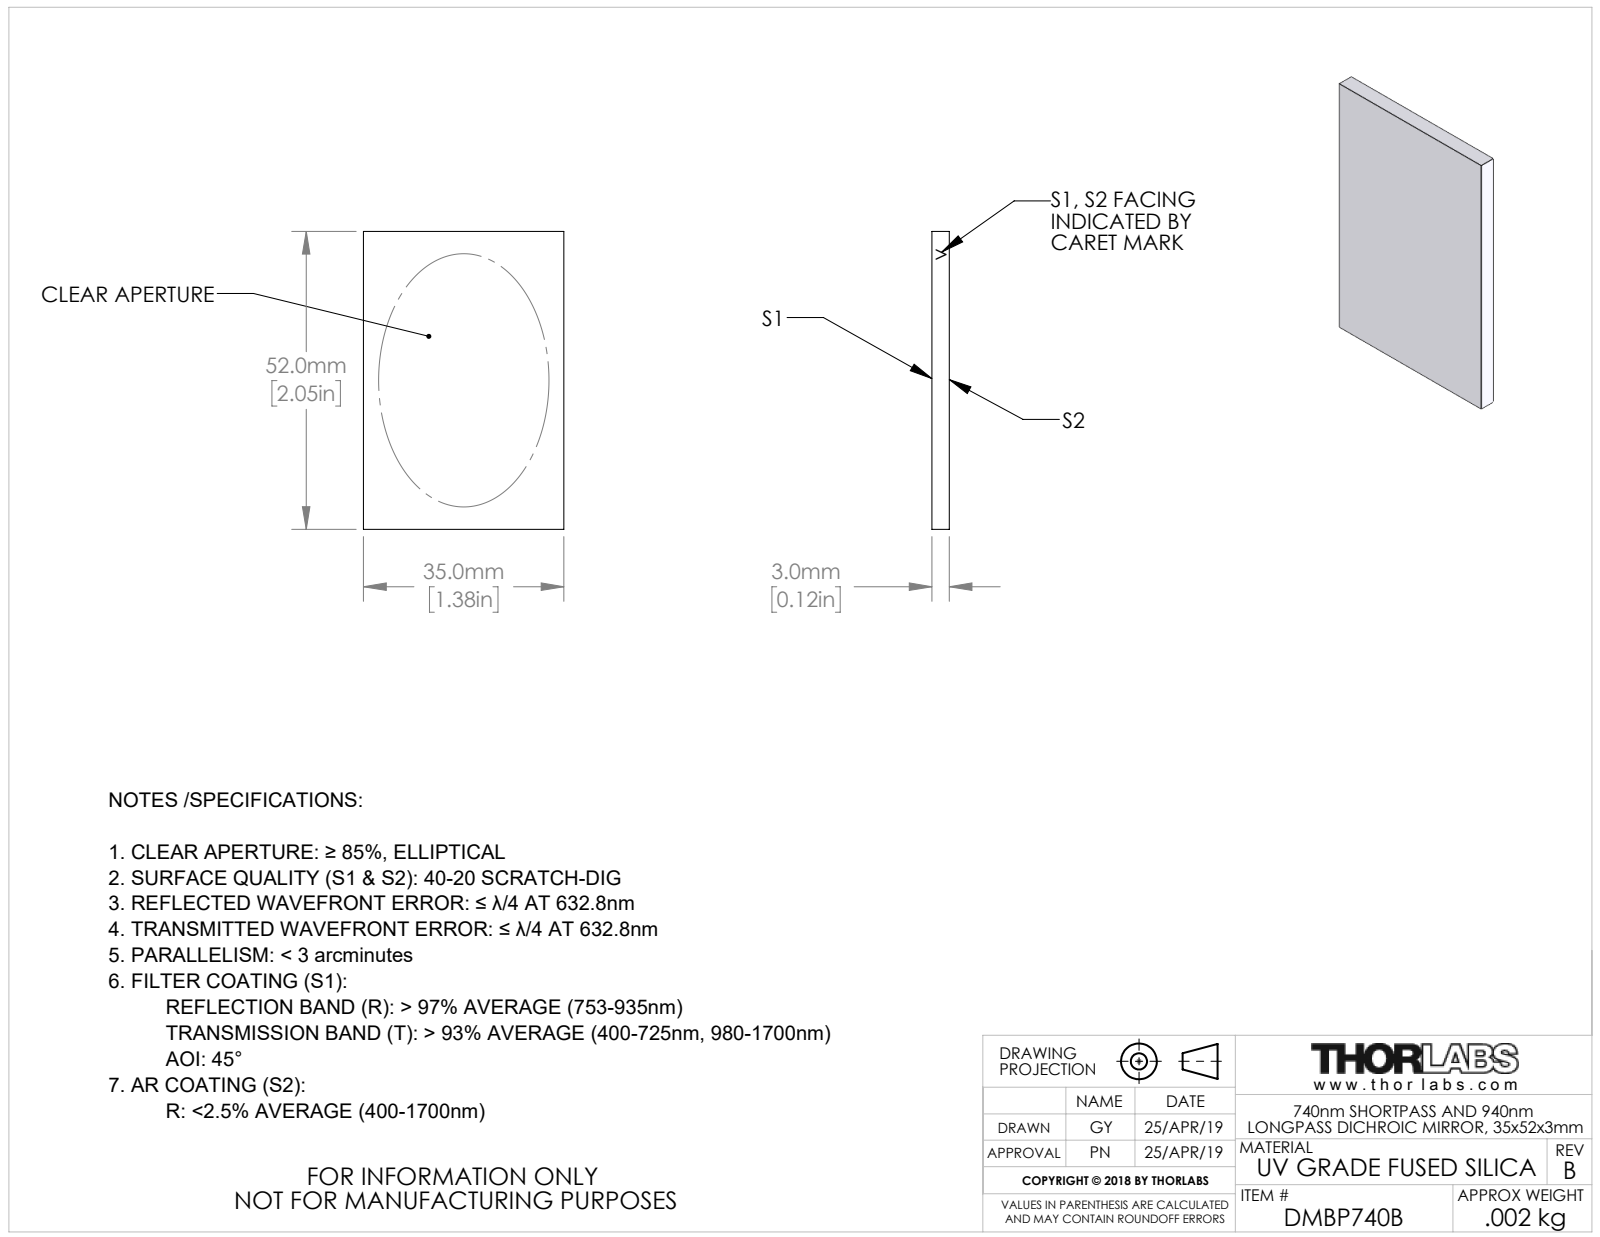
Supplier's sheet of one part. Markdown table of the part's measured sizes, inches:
| quantity | value |
| --- | --- |
| part name | TTN166726-E0W |
| STEP written by | SolidWorks 2018 (AUTOMOTIVE_DESIGN) |
| units | inches |
| bodies | 1 solid, 6 faces (6 planar, 0 cylindrical, 0 other) |
| overall size | 2.047 × 1.378 × 0.118 |
| volume | 0.333 in³ |
| surface area | 6.451 in² |
| main face-to-face distances | 0.118, 1.378, 2.047 |
